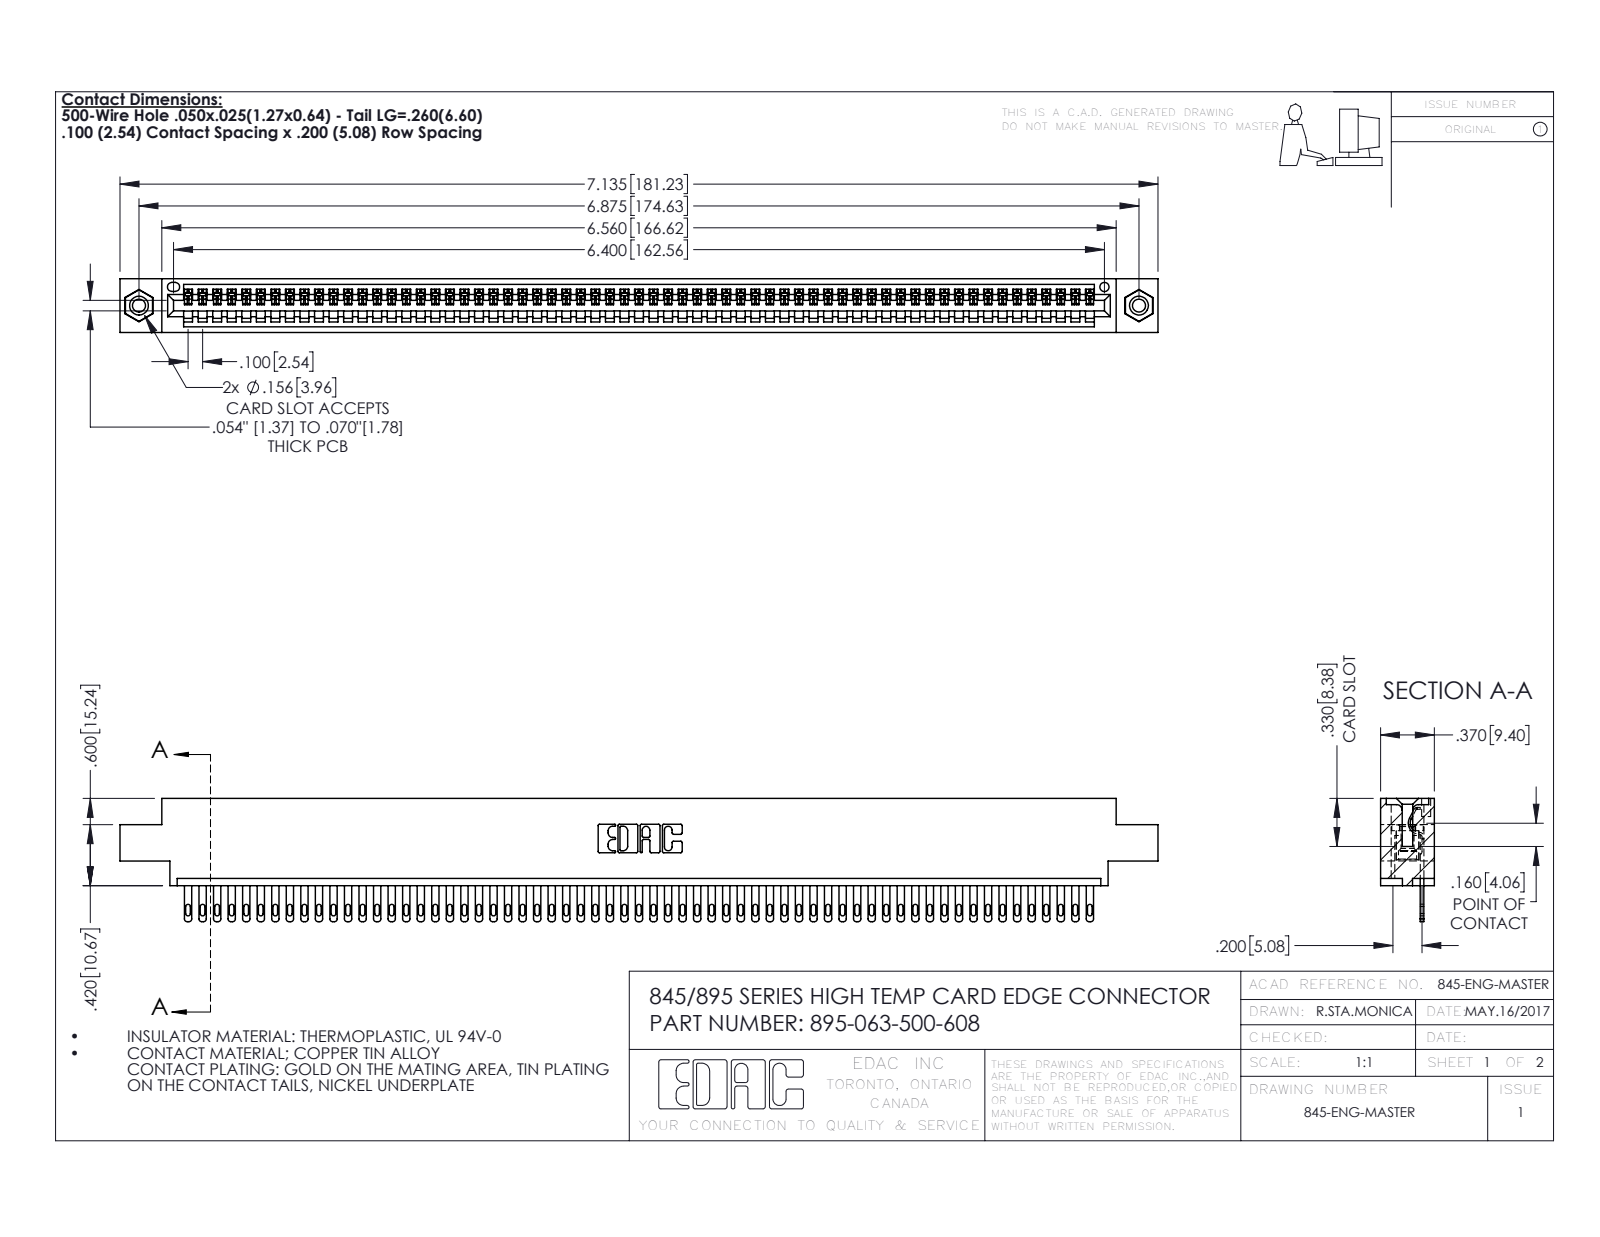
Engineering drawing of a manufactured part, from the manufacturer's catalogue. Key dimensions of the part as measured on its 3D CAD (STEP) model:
Part name (STEP PRODUCT): 345-292-001_345-293-100; 345-250-001_345-250-003-102; 895-063-500-608; 845 Part_0.170 Offset - 0.156 Dia-TI
STEP written by: SolidWorks 2020 (CONFIG_CONTROL_DESIGN)
Units: inches
Bodies: 66 solids, 3592 faces (2258 planar, 1318 cylindrical, 16 other)
Overall size (bounding box): 7.135 × 0.847 × 0.37
Volume: 1.056 in³ · Surface area: 36.53 in²
Round holes (diameter × count): ⌀0.089 ×2, ⌀0.125 ×2, ⌀0.156 ×2, ⌀0.064 ×1
Round bosses / shafts (diameter × count): ⌀0.155 ×2
Partial cylindrical surfaces — rounded edges, fillets, slot ends (radius × count): R0.006 ×126, R0.016 ×126, R0.02 ×126, R0.01 ×22, R0.007 ×6, R0.031 ×6, R0.026 ×3, R0.031 ×2
Main face-to-face distances: 0.072, 0.298, 0.37, 0.098, 0.272, 0.025, 0.2, 0.225, 0.175, 0.149
Hole centre spacings: 0.27, 6.639, 6.875
